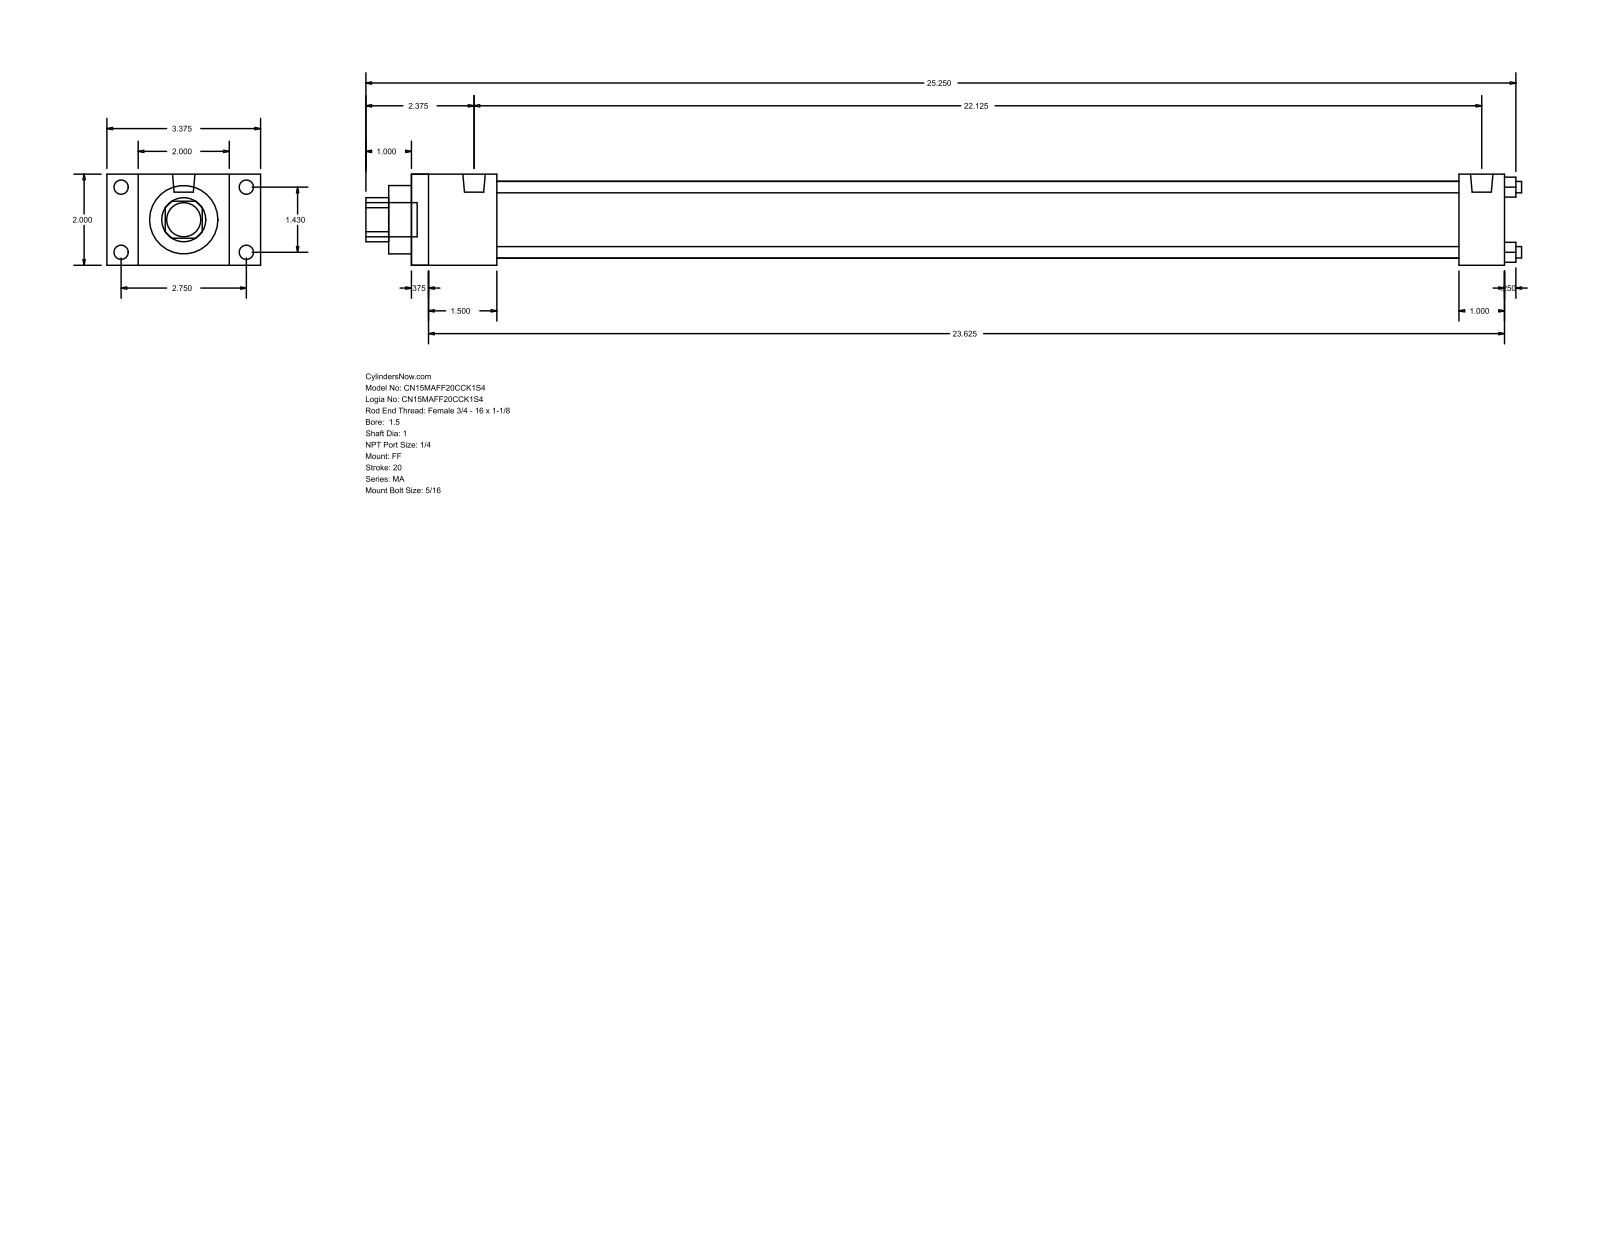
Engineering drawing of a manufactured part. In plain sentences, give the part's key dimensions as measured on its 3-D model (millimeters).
The part is named "MA_FF__0150_1". Its 3-D file was written by "GSSL Pune (CONFIG_CONTROL_DESIGN)". It is 0 solids with 92 faces: 64 planar, 28 cylindrical and 0 other. Overall it measures 644.52 by 85.72 by 50.8 millimeters. Round holes: 4 of diameter 6.35, 1 of diameter 25.4, 1 of diameter 38.1, 1 of diameter 42.93. Round bosses or shafts: 8 of diameter 7.94, 2 of diameter 12.49, 1 of diameter 19.05. Partial cylindrical surfaces (rounded edges, fillets, slot ends): 1 of radius 12.29. The main face-to-face distances are 50.8, 609.6, 9.52, 600.08, 25.4, 47.63, 584.2, 38.11, 574.68, 536.57. The hole center spacings are 25.68, 36.32, 51.36.
